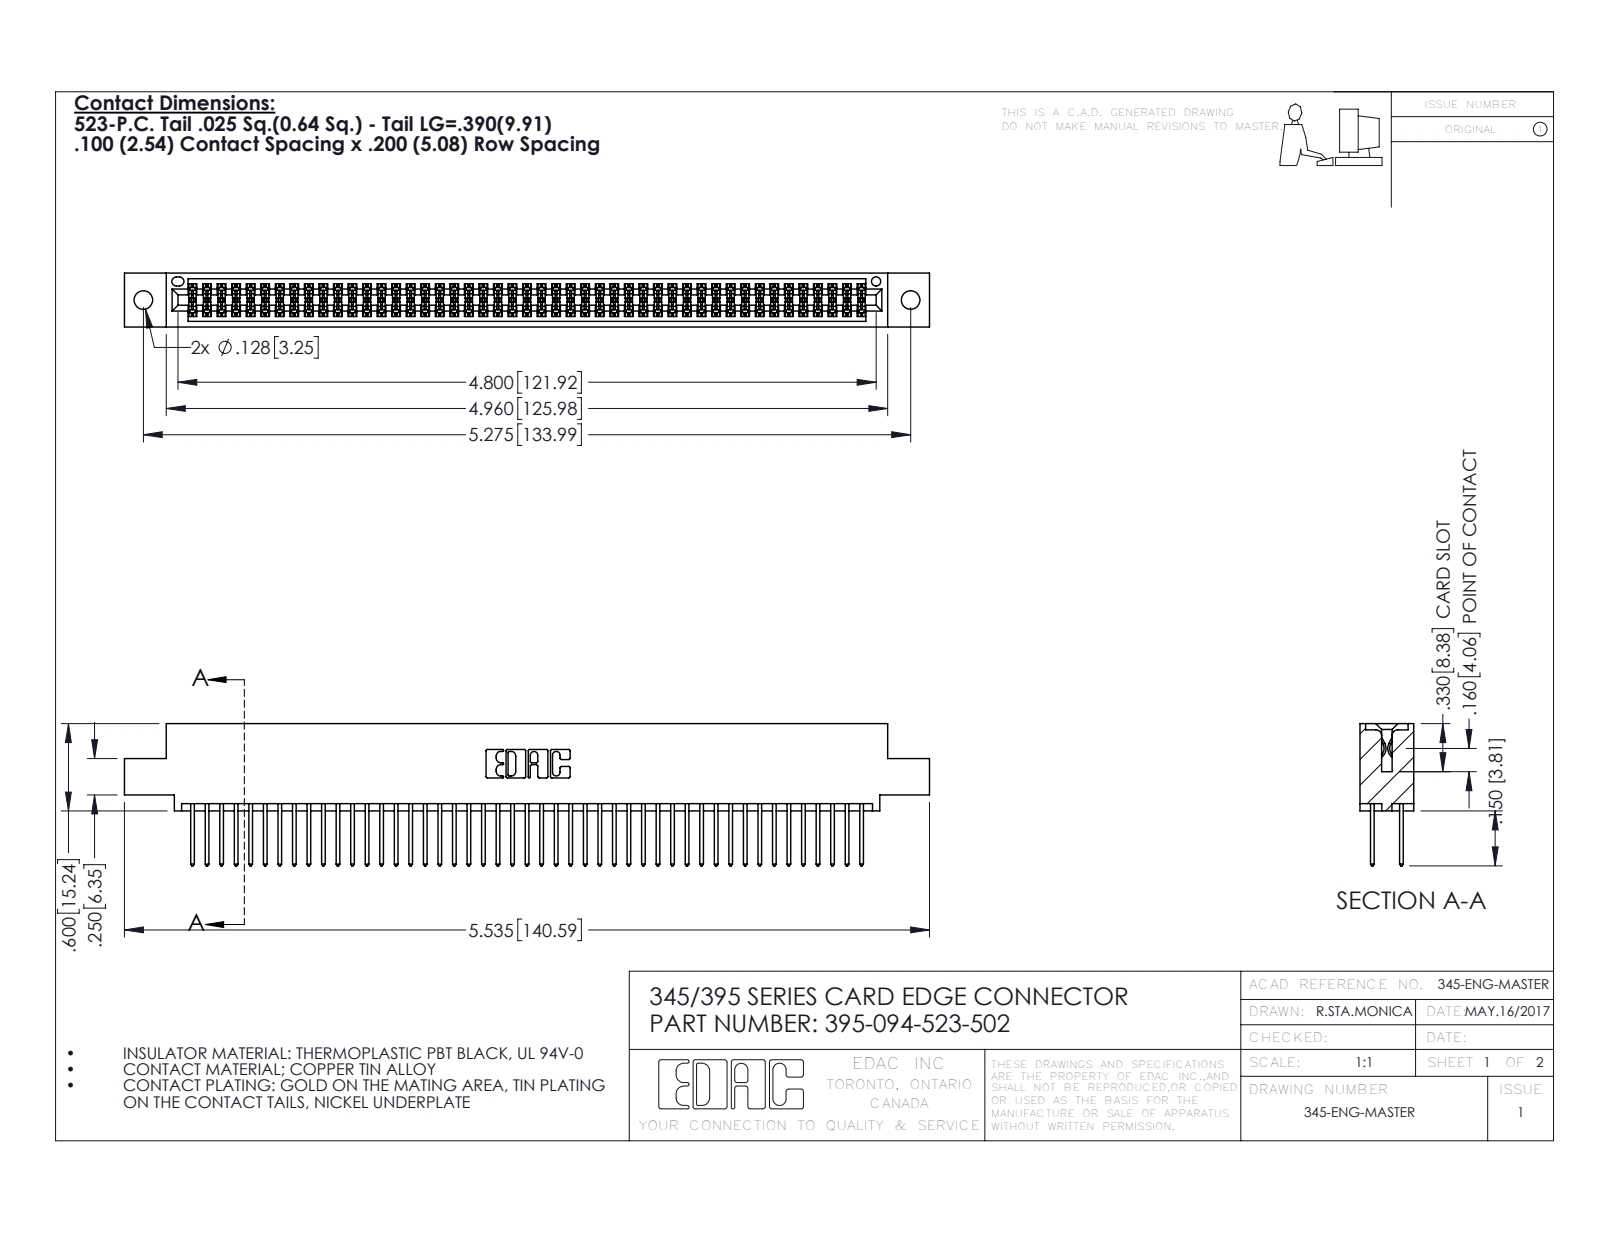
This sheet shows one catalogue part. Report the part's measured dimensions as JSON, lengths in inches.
{"part_name": "345 Part_0.110 Offset - 0.128 Dia; 395-094-523-502; 345-292-001_345-293-123", "step_written_by": "SolidWorks 2016 (CONFIG_CONTROL_DESIGN)", "units": "inches", "bodies": {"solids": 95, "faces": 4830, "planar": 3186, "cylindrical": 1644, "other": 0}, "overall_size": [5.535, 0.977, 0.37], "volume_in3": 0.841, "surface_area_in2": 32.8, "round_holes": [[0.128, 2], [0.064, 1]], "partial_cylinders_radius": [[0.006, 141], [0.01, 94], [0.01, 22], [0.007, 6], [0.031, 6], [0.026, 3], [0.014, 2], [0.019, 2]], "face_to_face_distances": [0.298, 0.072, 0.2, 0.098, 0.272, 0.025, 0.37, 0.225, 0.175, 0.149], "hole_center_spacings": [0.27, 5.039, 5.275]}
